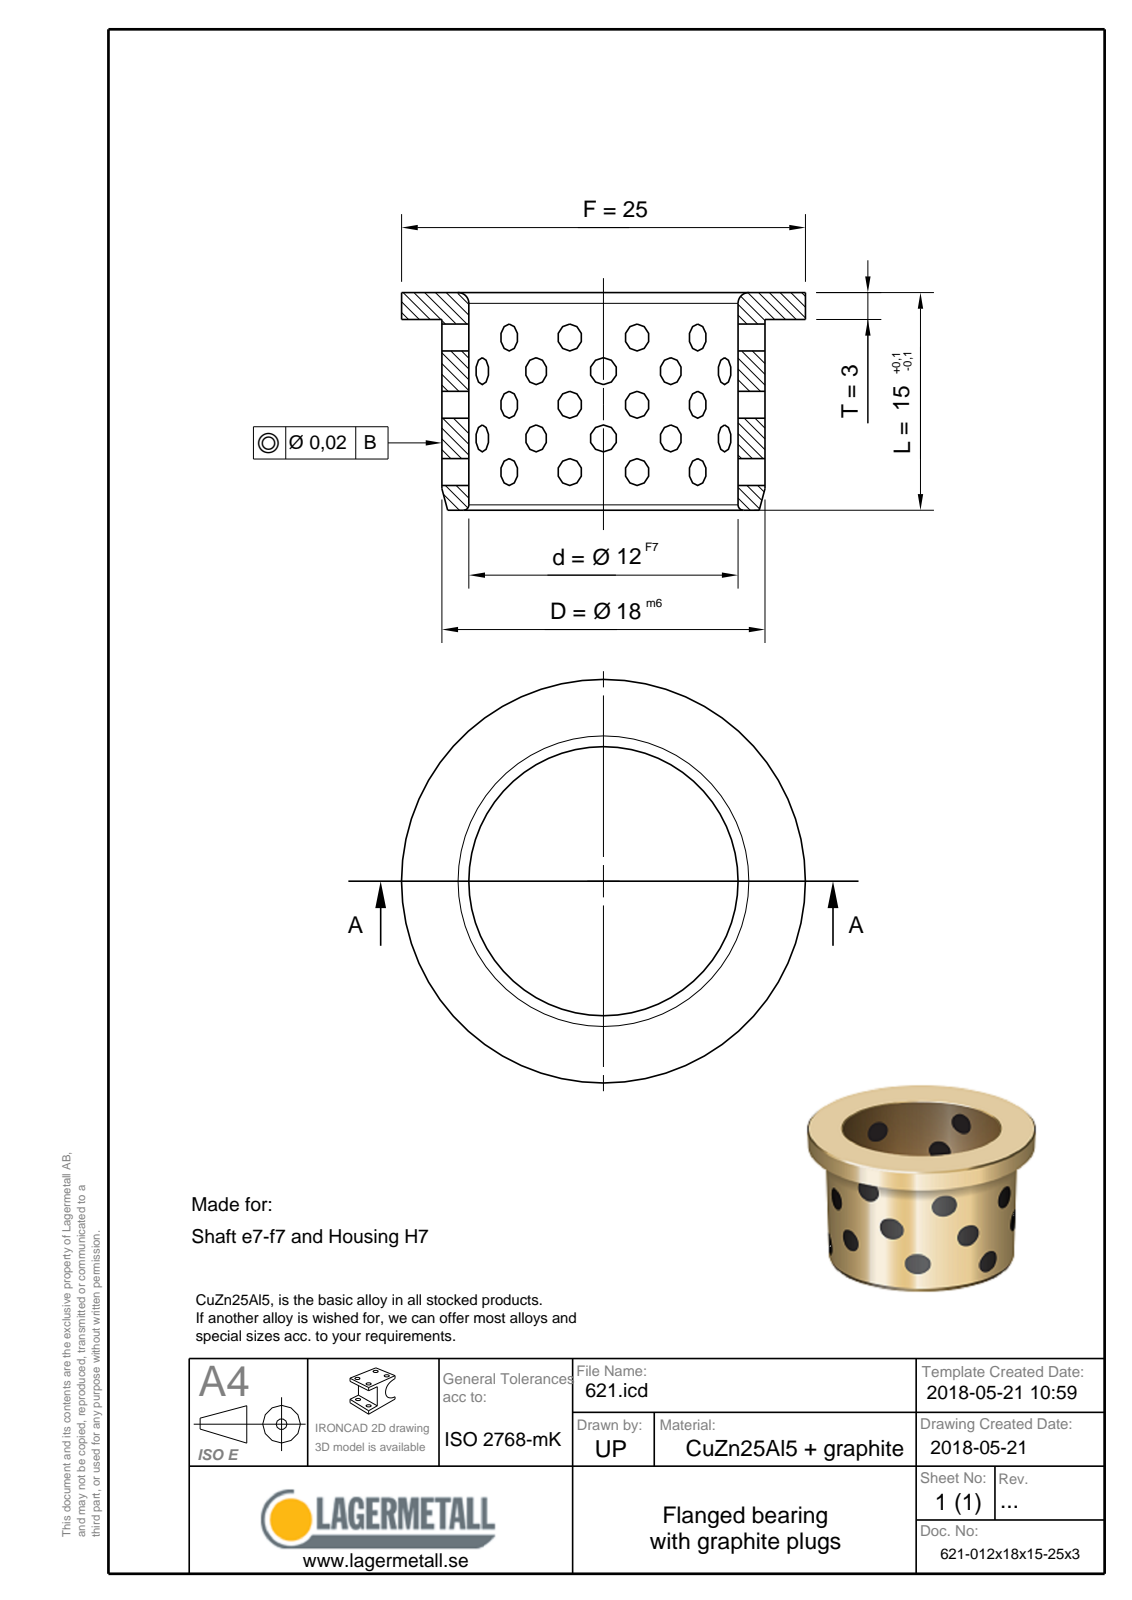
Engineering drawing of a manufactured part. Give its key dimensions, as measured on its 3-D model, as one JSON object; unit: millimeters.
{"part_name": "621-012x18x15-25x3", "step_written_by": "Spatial InterOp 3D (CONFIG_CONTROL_DESIGN)", "units": "millimeters", "bodies": {"solids": 1, "faces": 9, "planar": 3, "cylindrical": 3, "other": 3}, "overall_size": [25, 25, 15], "volume_mm3": 2758, "surface_area_mm2": 2162, "round_holes": [[12, 1]], "round_bosses_or_shafts": [[25, 1], [18, 1]], "face_to_face_distances": [3, 12, 15]}
